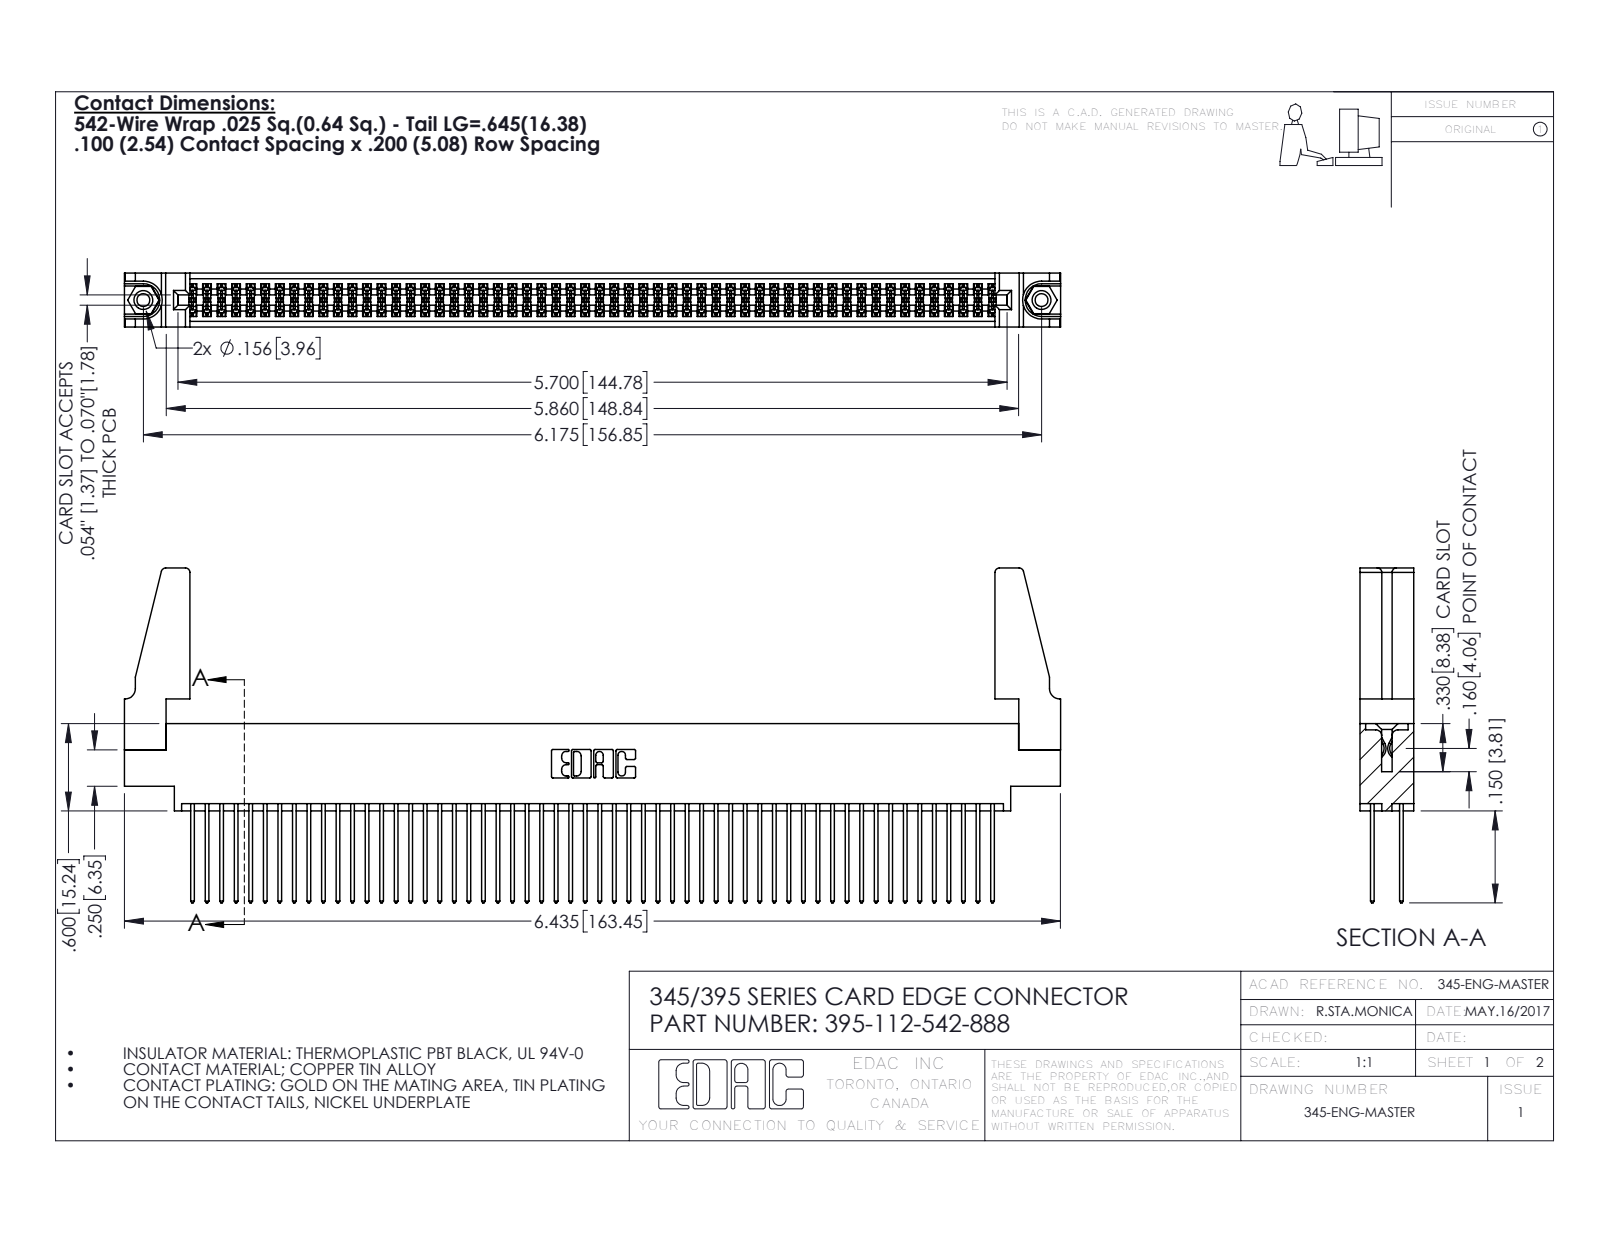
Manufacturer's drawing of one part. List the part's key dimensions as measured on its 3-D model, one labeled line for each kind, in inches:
Part name (STEP PRODUCT): 345-292-001_345-293-142; 345-220-078_345-220-088; 345 Part_0.170 Offset - 0.156 Dia-TH; 345-250-001_345-250-001-102 (+1 more)
STEP written by: SolidWorks 2016 (CONFIG_CONTROL_DESIGN)
Units: inches
Bodies: 117 solids, 5854 faces (3852 planar, 1986 cylindrical, 16 other)
Overall size (bounding box): 6.436 × 2.302 × 0.37
Volume: 1.2 in³ · Surface area: 46.88 in²
Round holes (diameter × count): ⌀0.089 ×2, ⌀0.125 ×2, ⌀0.156 ×2, ⌀0.064 ×1
Round bosses / shafts (diameter × count): ⌀0.155 ×2
Partial cylindrical surfaces — rounded edges, fillets, slot ends (radius × count): R0.006 ×168, R0.01 ×112, R0.01 ×22, R0.03 ×8, R0.007 ×6, R0.031 ×6, R0.026 ×3, R0.014 ×2
Main face-to-face distances: 0.072, 0.298, 0.2, 0.098, 0.272, 0.025, 0.37, 0.225, 0.175, 0.149
Hole centre spacings: 0.27, 5.939, 6.175
